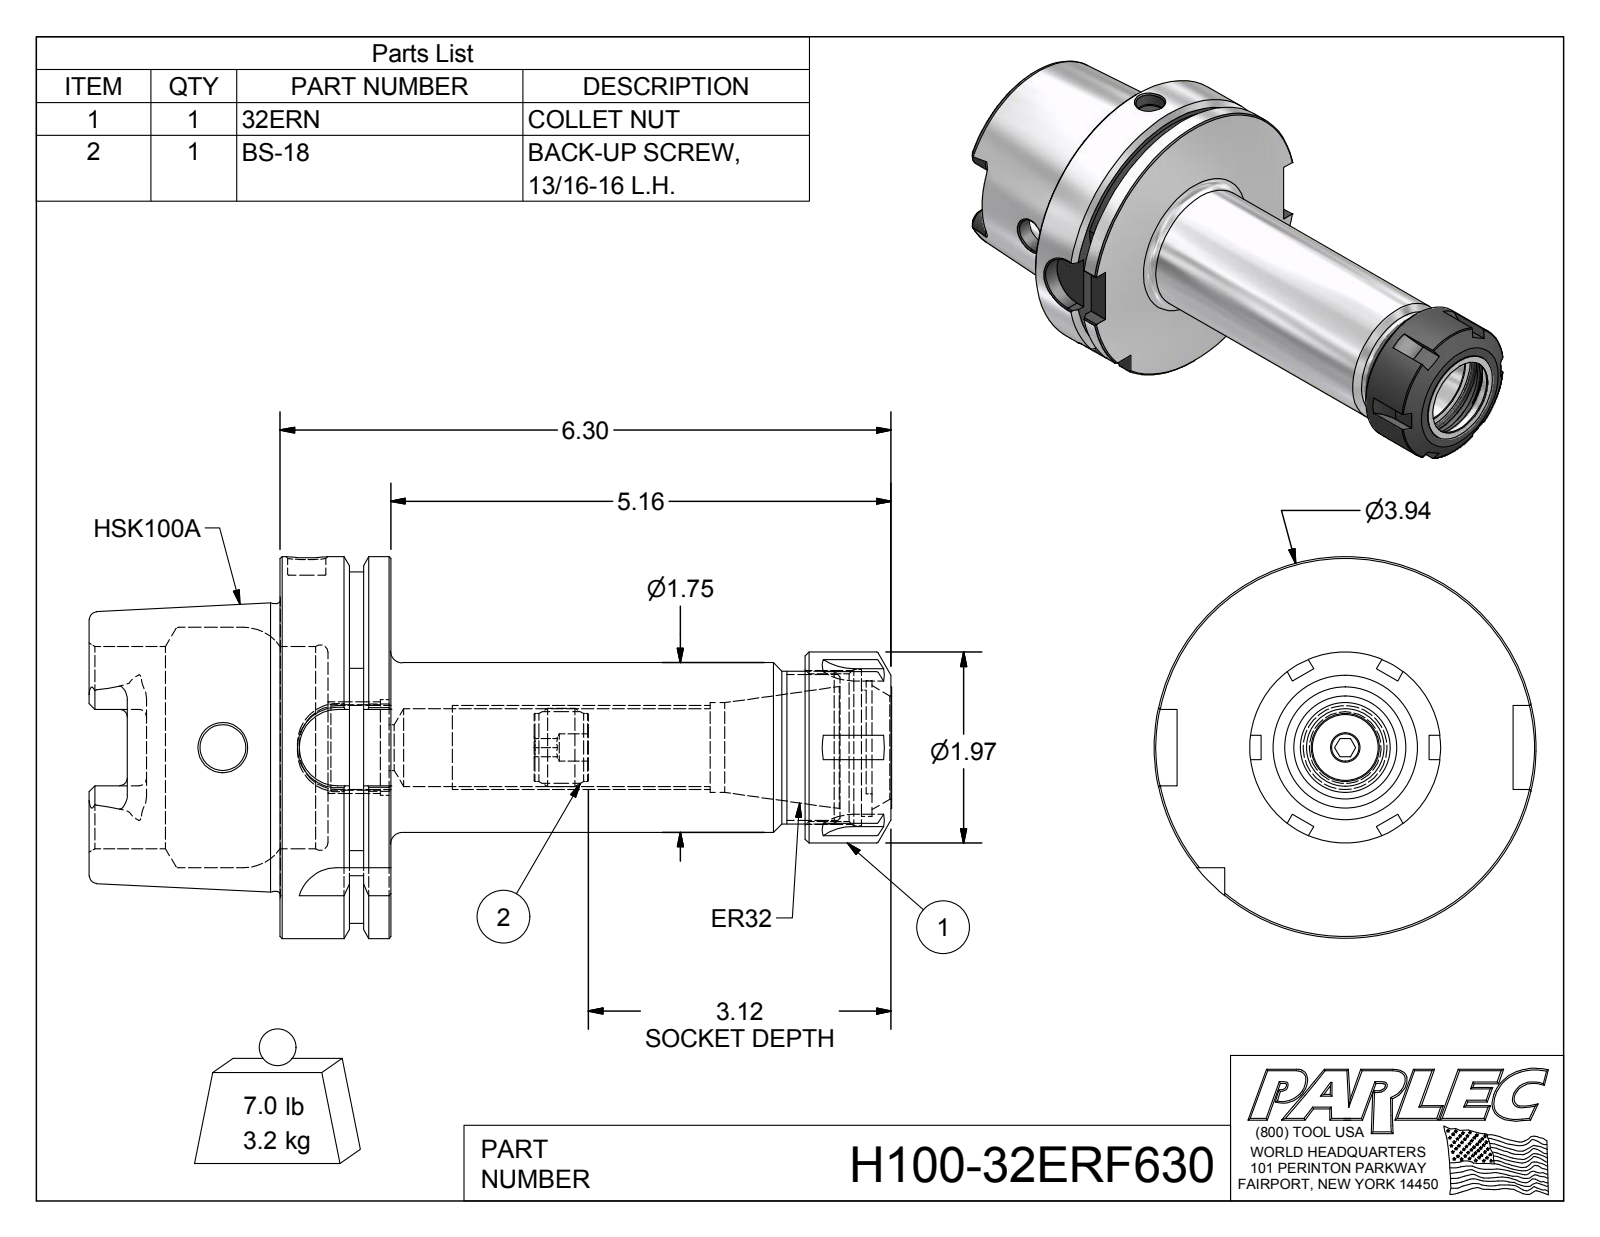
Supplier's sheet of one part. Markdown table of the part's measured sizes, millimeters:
| quantity | value |
| --- | --- |
| part name | H100-32ER630-1; 32ERN; BS-18; H100-32ERF630 |
| STEP written by | Autodesk Inventor 2016 (AUTOMOTIVE_DESIGN) |
| units | millimeters |
| bodies | 3 solids, 234 faces (84 planar, 60 cylindrical, 90 other) |
| overall size | 210.02 × 100 × 100 |
| volume | 406 779 mm³ |
| surface area | 83 956 mm² |
| round holes (diameter × count) | 9 × 2, 12 × 2, 7.11 × 1, 10 × 1, 20.37 × 1, 22.38 × 1, 23.5 × 1, 25.02 × 1, 27 × 1, 33.02 × 1, 38.65 × 1, 41 × 1 |
| round bosses / shafts (diameter × count) | 100 × 1, 92 × 1, 75.36 × 1, 50 × 1, 44.45 × 1, 40 × 1, 20.45 × 1, 17.78 × 1 |
| partial cylindrical surfaces (radius × count) | 0.51 × 12, 2 × 6, 4.88 × 4, 10 × 4, 14.9 × 1, 17.5 × 1 |
| main face-to-face distances | 29, 12.5, 16.5, 50, 62.5, 79, 210.02, 160.02, 147.52, 131.02 |
| hole center spacings | 1.85 |
